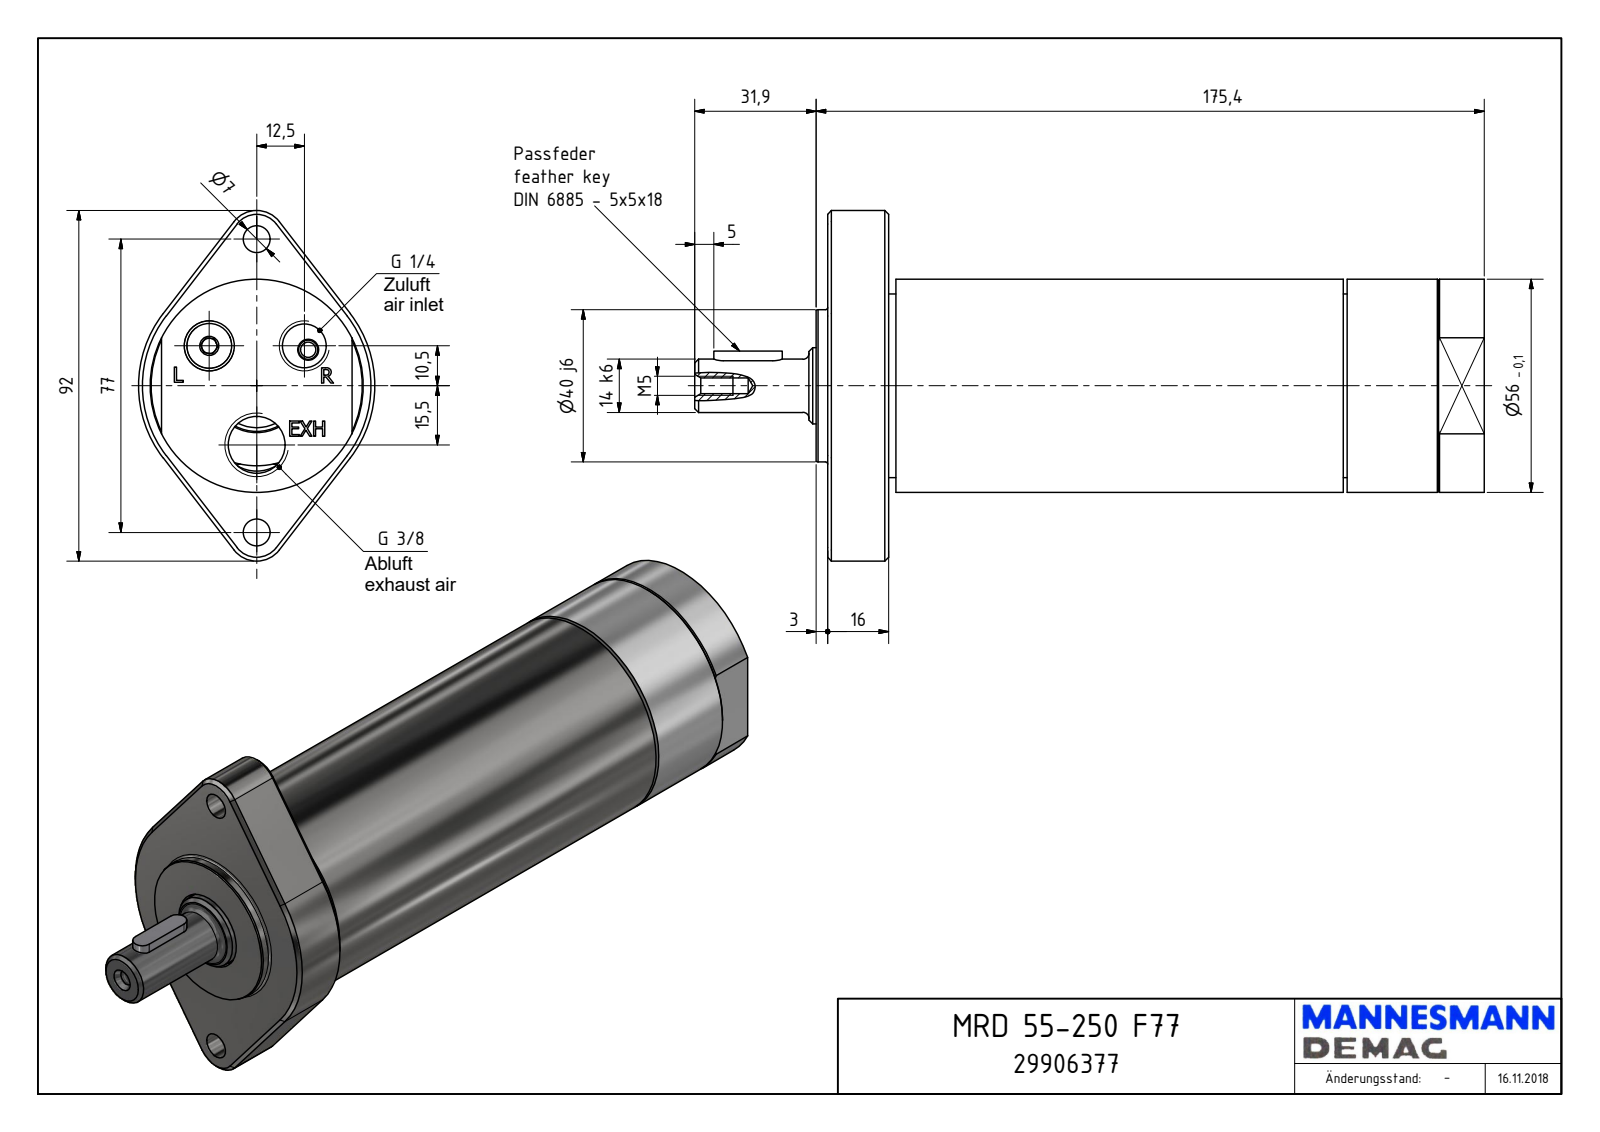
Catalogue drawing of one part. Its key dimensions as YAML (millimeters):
part_name: "MRD 55-250 F77_29906377"
step_written_by: "Autodesk Inventor 2018 (AUTOMOTIVE_DESIGN)"
units: millimeters
bodies: {solids: 1, faces: 227, planar: 131, cylindrical: 47, other: 49}
overall_size: [207.3, 92, 62]
volume: 443973
surface_area: 55797
round_holes:
  - {diameter: 7, count: 2}
  - {diameter: 4, count: 1}
  - {diameter: 4.13, count: 1}
  - {diameter: 11.45, count: 1}
  - {diameter: 14.95, count: 1}
  - {diameter: 21, count: 1}
  - {diameter: 21.25, count: 1}
  - {diameter: 23.54, count: 1}
  - {diameter: 26, count: 1}
  - {diameter: 48.38, count: 1}
round_bosses_or_shafts:
  - {diameter: 56, count: 1}
  - {diameter: 48.18, count: 1}
  - {diameter: 40, count: 1}
  - {diameter: 19.95, count: 1}
  - {diameter: 14, count: 1}
partial_cylinders:
  - {radius: 10, count: 6}
  - {radius: 2.5, count: 2}
  - {radius: 6, count: 2}
  - {radius: 7.5, count: 2}
  - {radius: 5.72, count: 1}
  - {radius: 19.18, count: 1}
  - {radius: 21.96, count: 1}
  - {radius: 23, count: 1}
face_to_face_distances: [172.4, 16, 156.4, 3, 19, 175.4, 1.9, 20.9, 17.9, 154.5]
hole_center_spacings: [16.32, 28.85, 30.66, 38.5, 50.57, 15.5, 23, 25]
